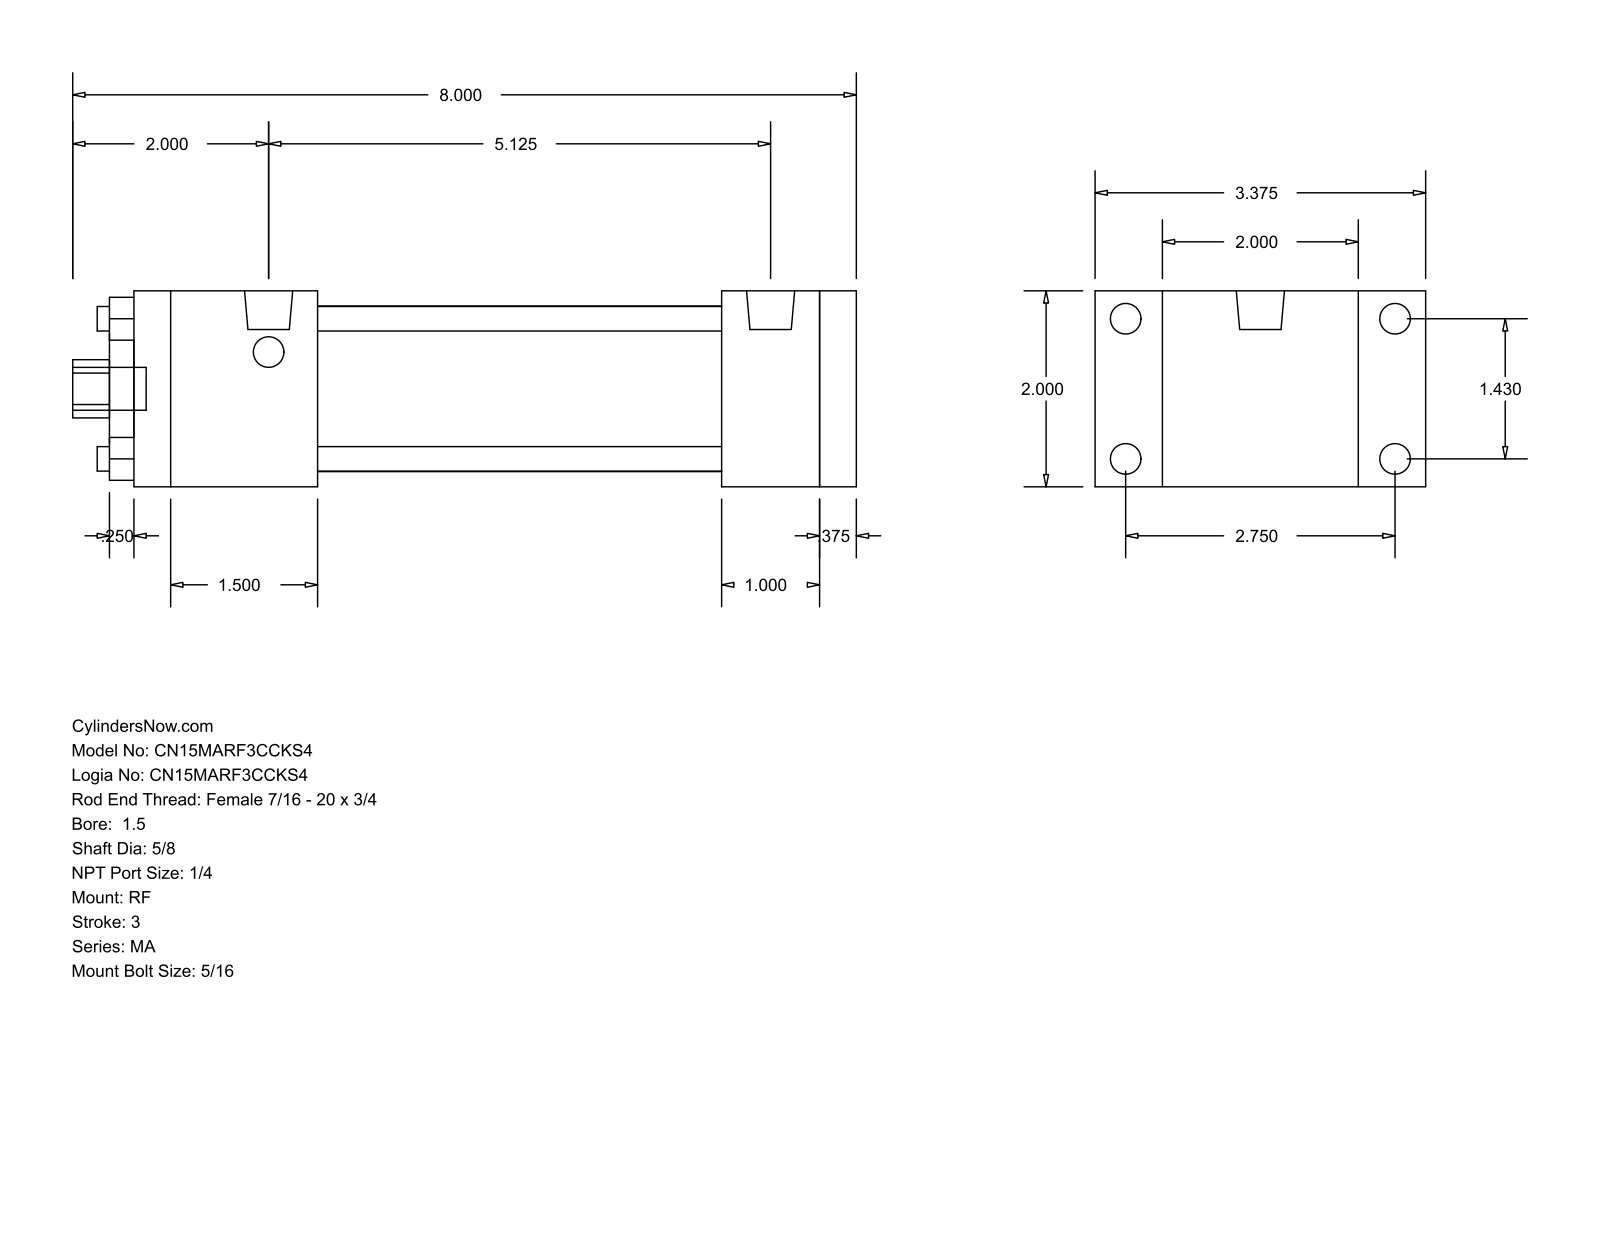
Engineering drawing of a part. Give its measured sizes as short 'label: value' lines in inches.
name: MA_RF__0150_0.625
written by: GSSL Pune (CONFIG_CONTROL_DESIGN)
unit: in
bodies: 0 solids, 92 faces (64 planar, 28 cylindrical, 0 other)
size: 8 × 3.375 × 2
holes: 4× ⌀0.25, 1× ⌀0.625, 1× ⌀1.125, 1× ⌀1.69
bosses: 8× ⌀0.313, 2× ⌀0.492, 1× ⌀0.437
rounds: 1× R0.297
face distances: 2, 0.375, 7, 7.375, 6, 1, 1.375, 1.875, 4.125, 5.125
hole spacings: 1.011, 1.43, 2.022
